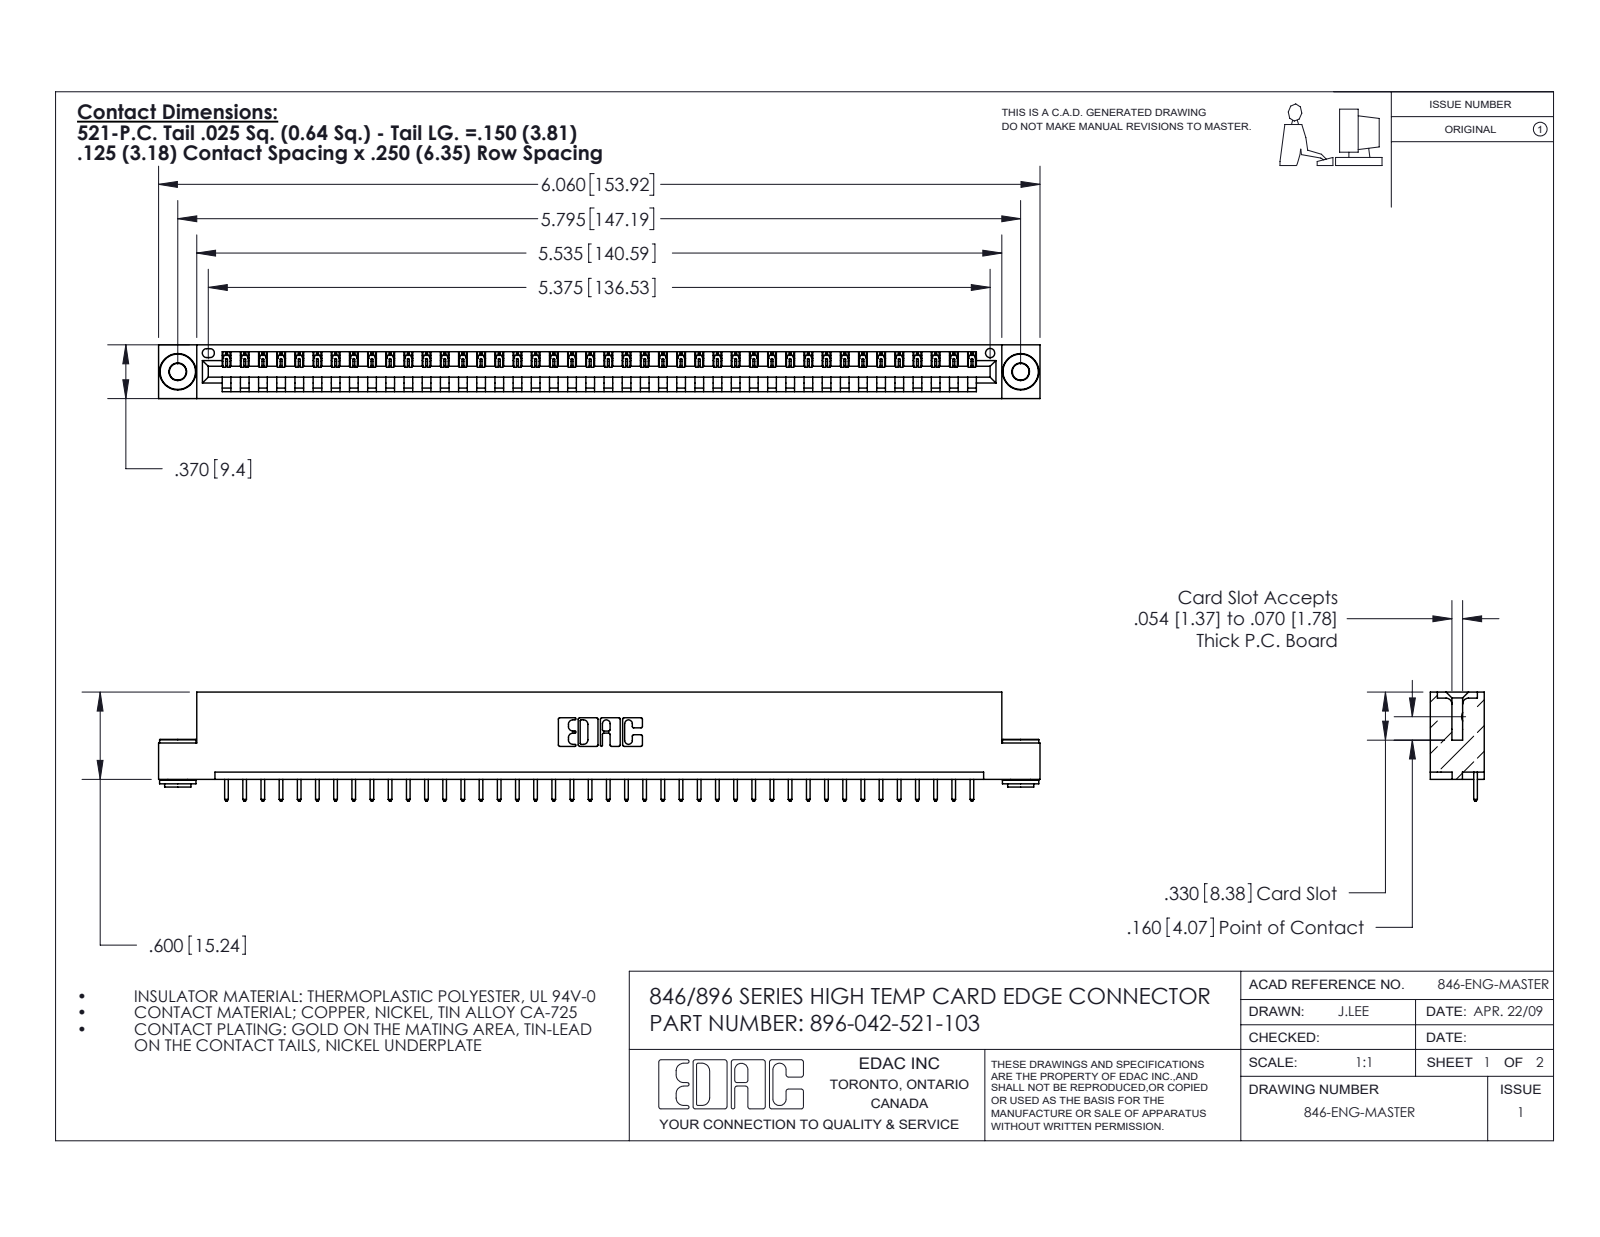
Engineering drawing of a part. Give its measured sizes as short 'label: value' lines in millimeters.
name: 345-292-001_345-293-121; 396-042-521-103; 345-250-002_345-250-002-102; 346 Part_Flush Mounting Lugs - 0.156 Dia-TH
written by: SolidWorks 2016 (CONFIG_CONTROL_DESIGN)
unit: mm
bodies: 45 solids, 2596 faces (1766 planar, 822 cylindrical, 8 other)
size: 153.9 × 19.1 × 9.4
volume: 14 600 mm³; area: 18 030 mm²
holes: 2× ⌀2.9, 2× ⌀4, 1× ⌀1.6
bosses: 2× ⌀6.4, 2× ⌀4.6, 2× ⌀3.5
rounds: 84× R0.2, 84× R0.3, 22× R0.3, 6× R0.2, 6× R0.8, 3× R0.7, 2× R0.8, 2× R1
face distances: 1.2, 8.2, 9.4, 6.4, 0.6, 1.8, 7.6, 3.8, 5.6, 2.5
hole spacings: 6.2, 141.9, 147.2
